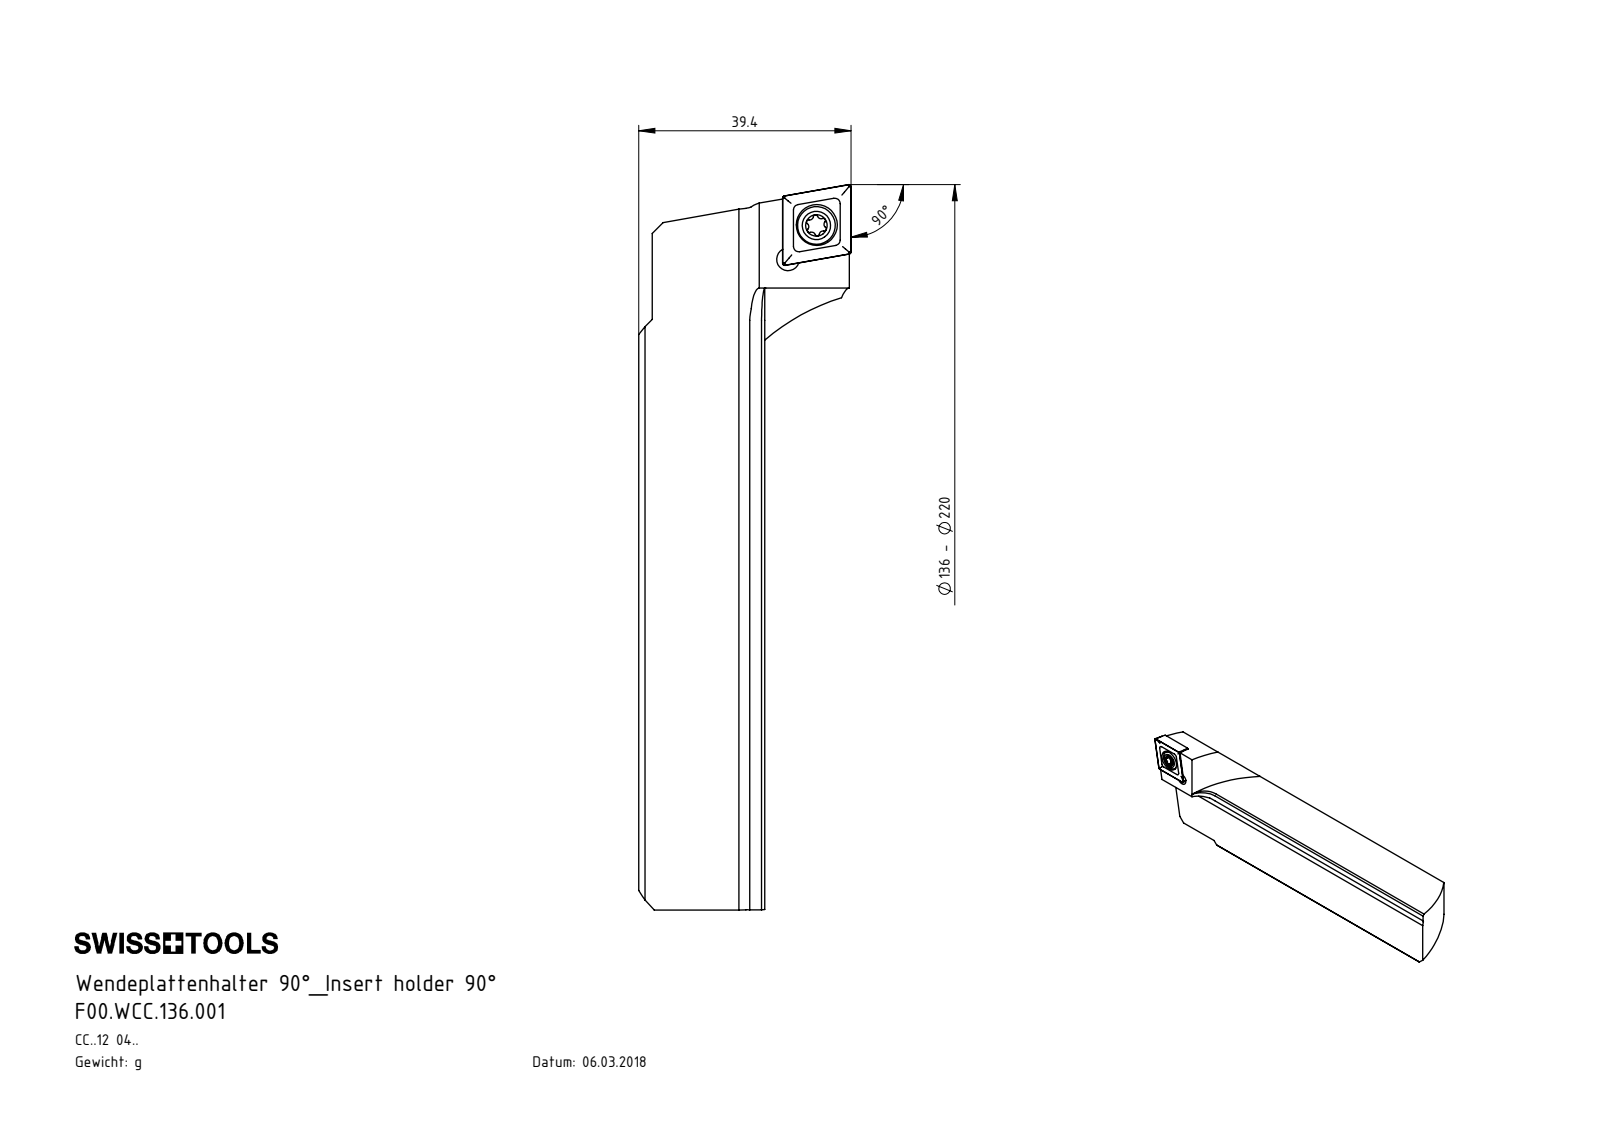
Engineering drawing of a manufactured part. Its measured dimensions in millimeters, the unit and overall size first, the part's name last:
Units: millimetres
Overall size (bounding box): 134.59 × 39.4 × 27.35
Round holes (diameter × count): ⌀4.2 ×2, ⌀5.5 ×1, ⌀7.6 ×1
Round bosses / shafts (diameter × count): ⌀7 ×1, ⌀5 ×1
Partial cylindrical surfaces — rounded edges, fillets, slot ends (radius × count): R0.2 ×8, R0.39 ×6, R0.69 ×4, R40 ×3, R0.69 ×2, R0.8 ×1, R6 ×1
Main face-to-face distances: 2.38, 4.76, 21.3, 7.14, 9.52, 4.77, 7.15, 9.53, 11.91, 14.29
Hole centre spacings: 8.21, 8.33
Volume: 55 816 mm³ · Surface area: 14 398 mm²
Bodies: 3 solids, 556 faces (342 planar, 40 cylindrical, 174 other)
Part name (STEP PRODUCT): F00-WCC.136.001_C; CCMT120404; WCC-ER2.001.010_A; F00.WCC.136.001
STEP written by: SolidWorks 2017 (CONFIG_CONTROL_DESIGN)
